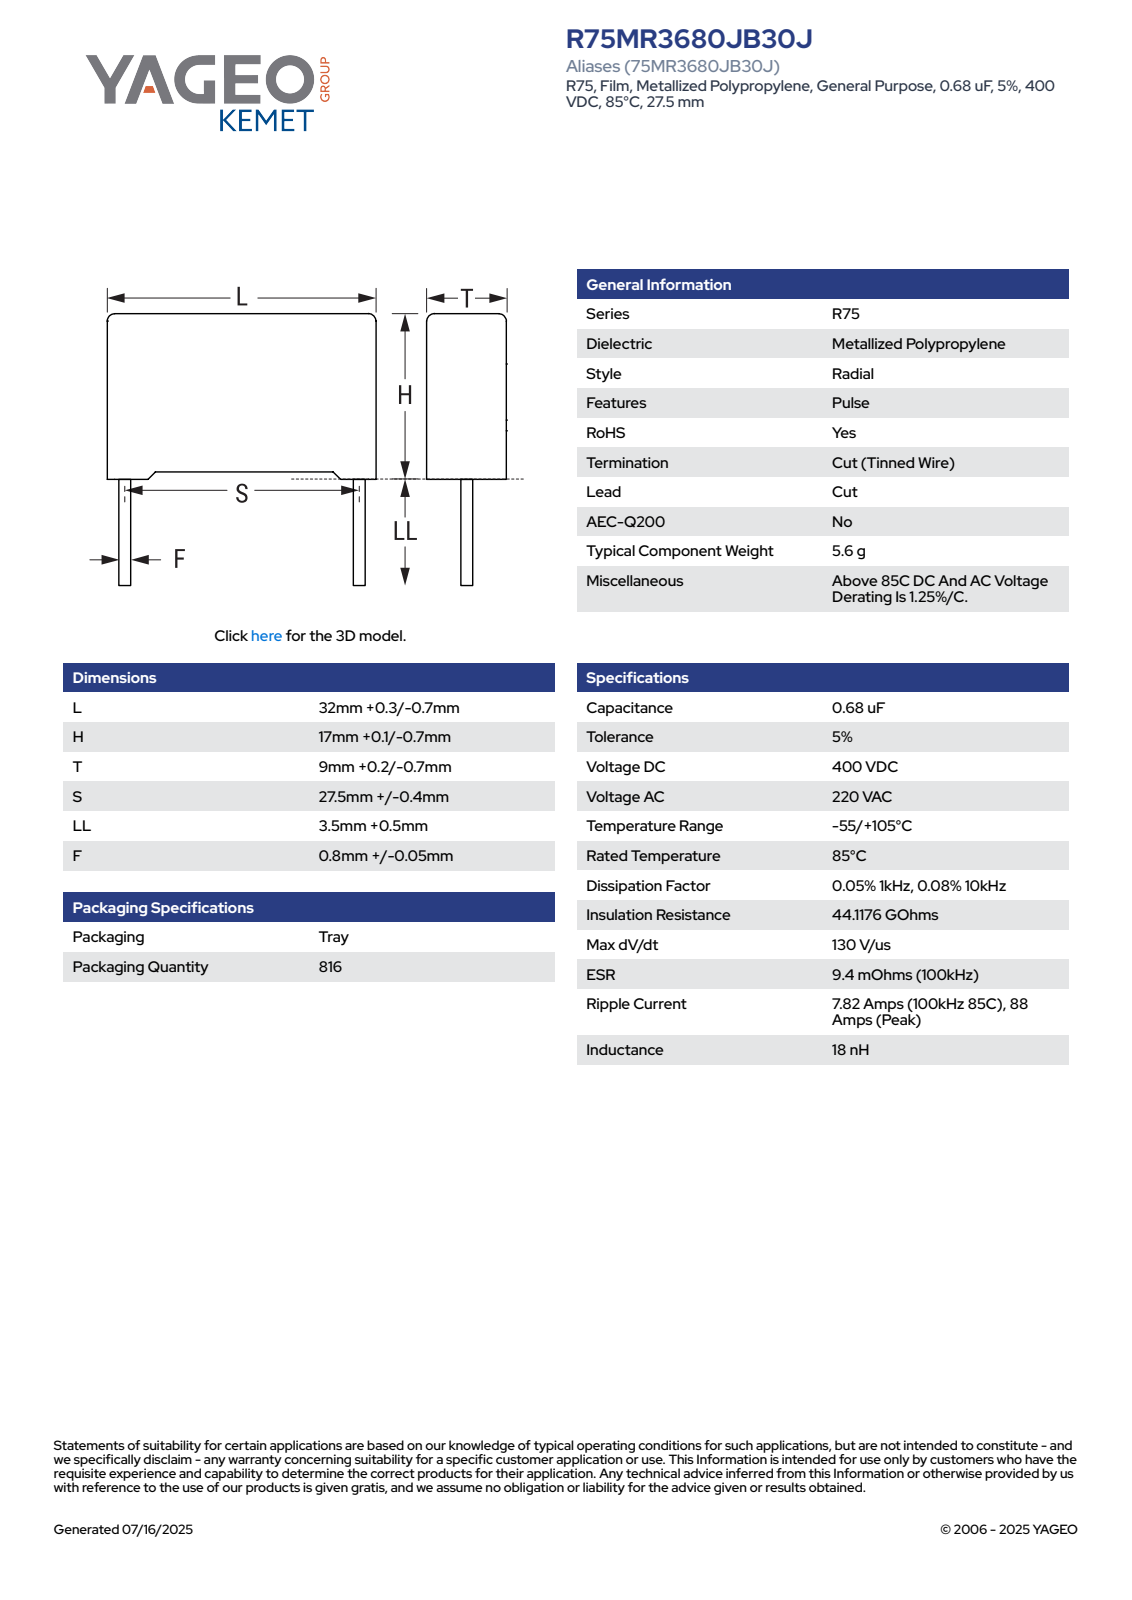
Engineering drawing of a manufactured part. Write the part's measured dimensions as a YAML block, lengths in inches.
part_name: "CFR_RB2_32X17X9_L32.3H17.1T9.2S27.5LL4F0.85"
step_written_by: "SolidWorks 2021 (AUTOMOTIVE_DESIGN)"
units: inches
bodies: {solids: 4, faces: 85, planar: 77, cylindrical: 8, other: 0}
overall_size: [1.272, 0.831, 0.363]
volume: 0.299
surface_area: 3.255
round_bosses_or_shafts:
  - {diameter: 0.033, count: 2}
partial_cylinders:
  - {radius: 0.02, count: 4}
face_to_face_distances: [0.362, 0.644, 1.272, 0.65, 0.023, 0.03, 0.673, 0.043, 0.363, 0.32]
